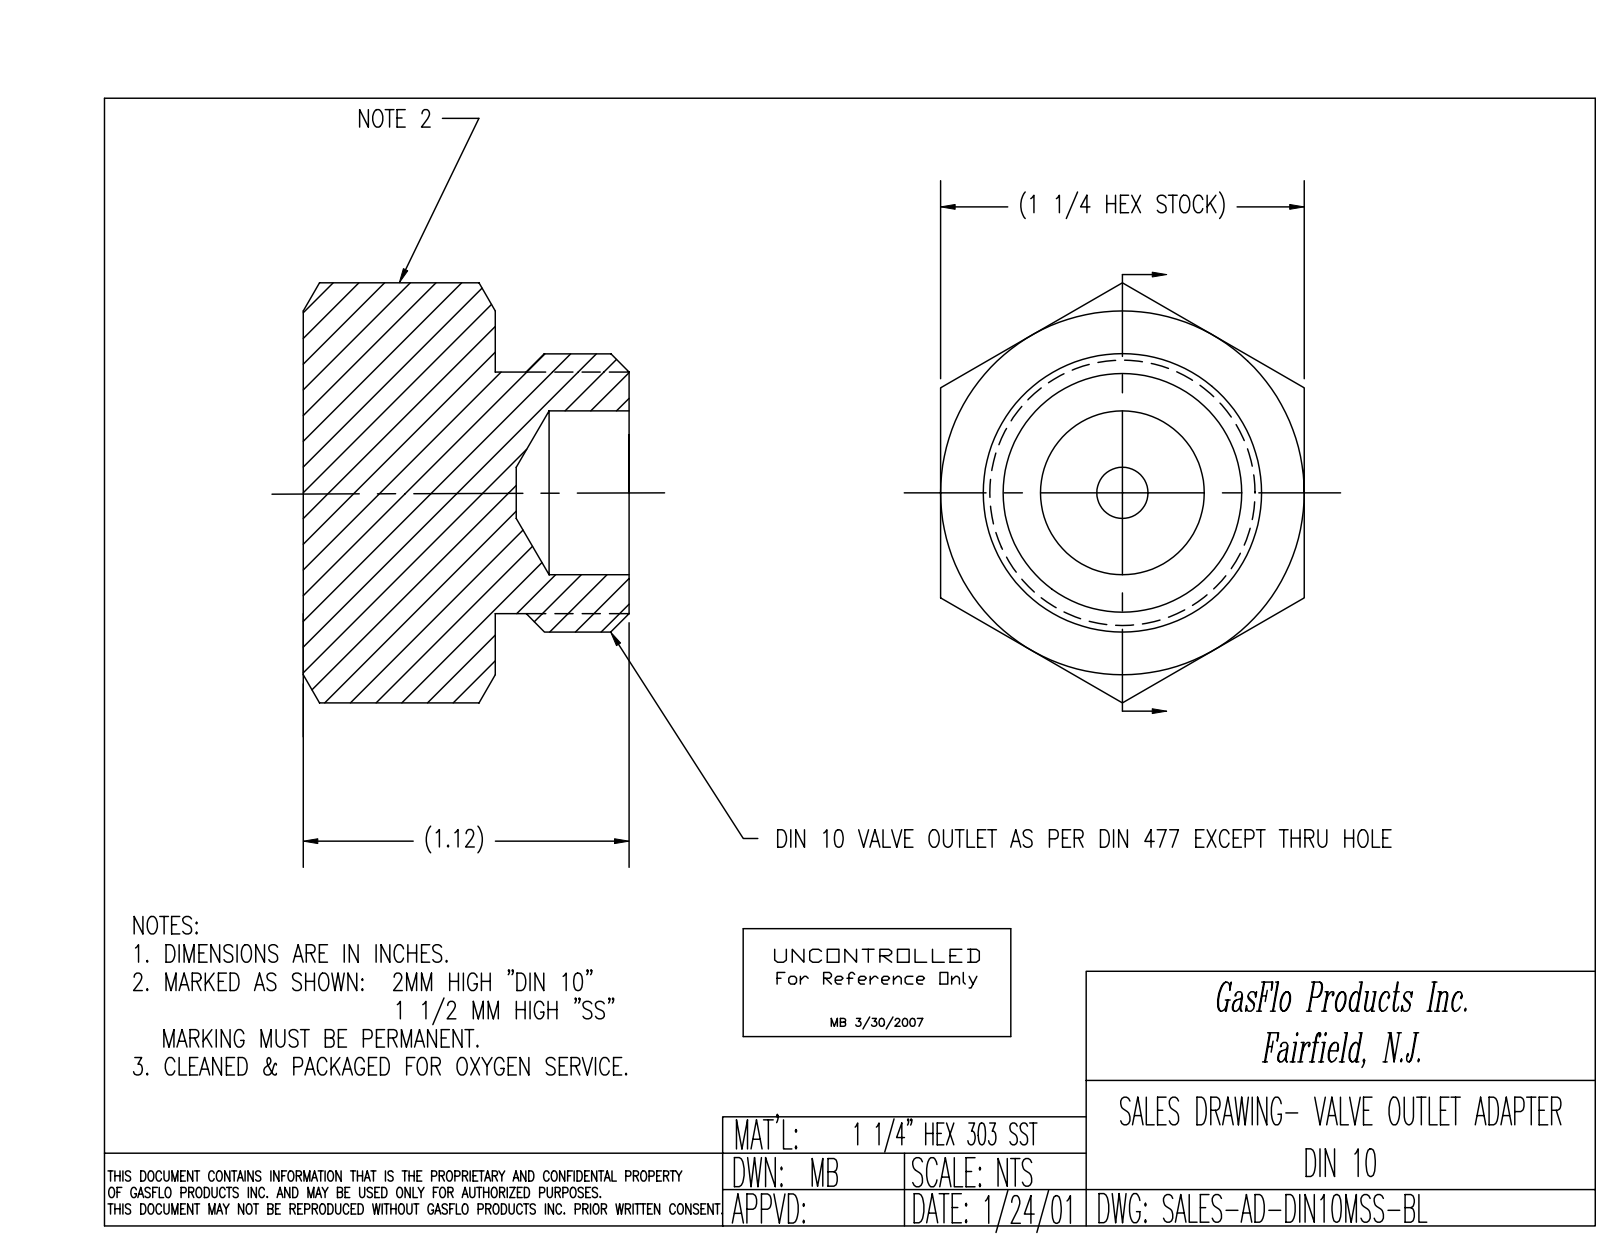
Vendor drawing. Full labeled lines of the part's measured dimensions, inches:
Part name (STEP PRODUCT): AD-DIN10MSS-BL
STEP written by: SolidWorks 2018 (CONFIG_CONTROL_DESIGN)
Units: inches
Bodies: 1 solid, 123 faces (49 planar, 12 cylindrical, 62 other)
Overall size (bounding box): 1.443 × 1.25 × 1.12
Volume: 1.088 in³ · Surface area: 7.898 in²
Round holes (diameter × count): ⌀0.551 ×1
Round bosses / shafts (diameter × count): ⌀0.949 ×1, ⌀0.82 ×1
Main face-to-face distances: 1.25, 0.66, 1.25, 0.46, 1.12, 0.732, 0.072, 0.387, 1.245, 0.153
